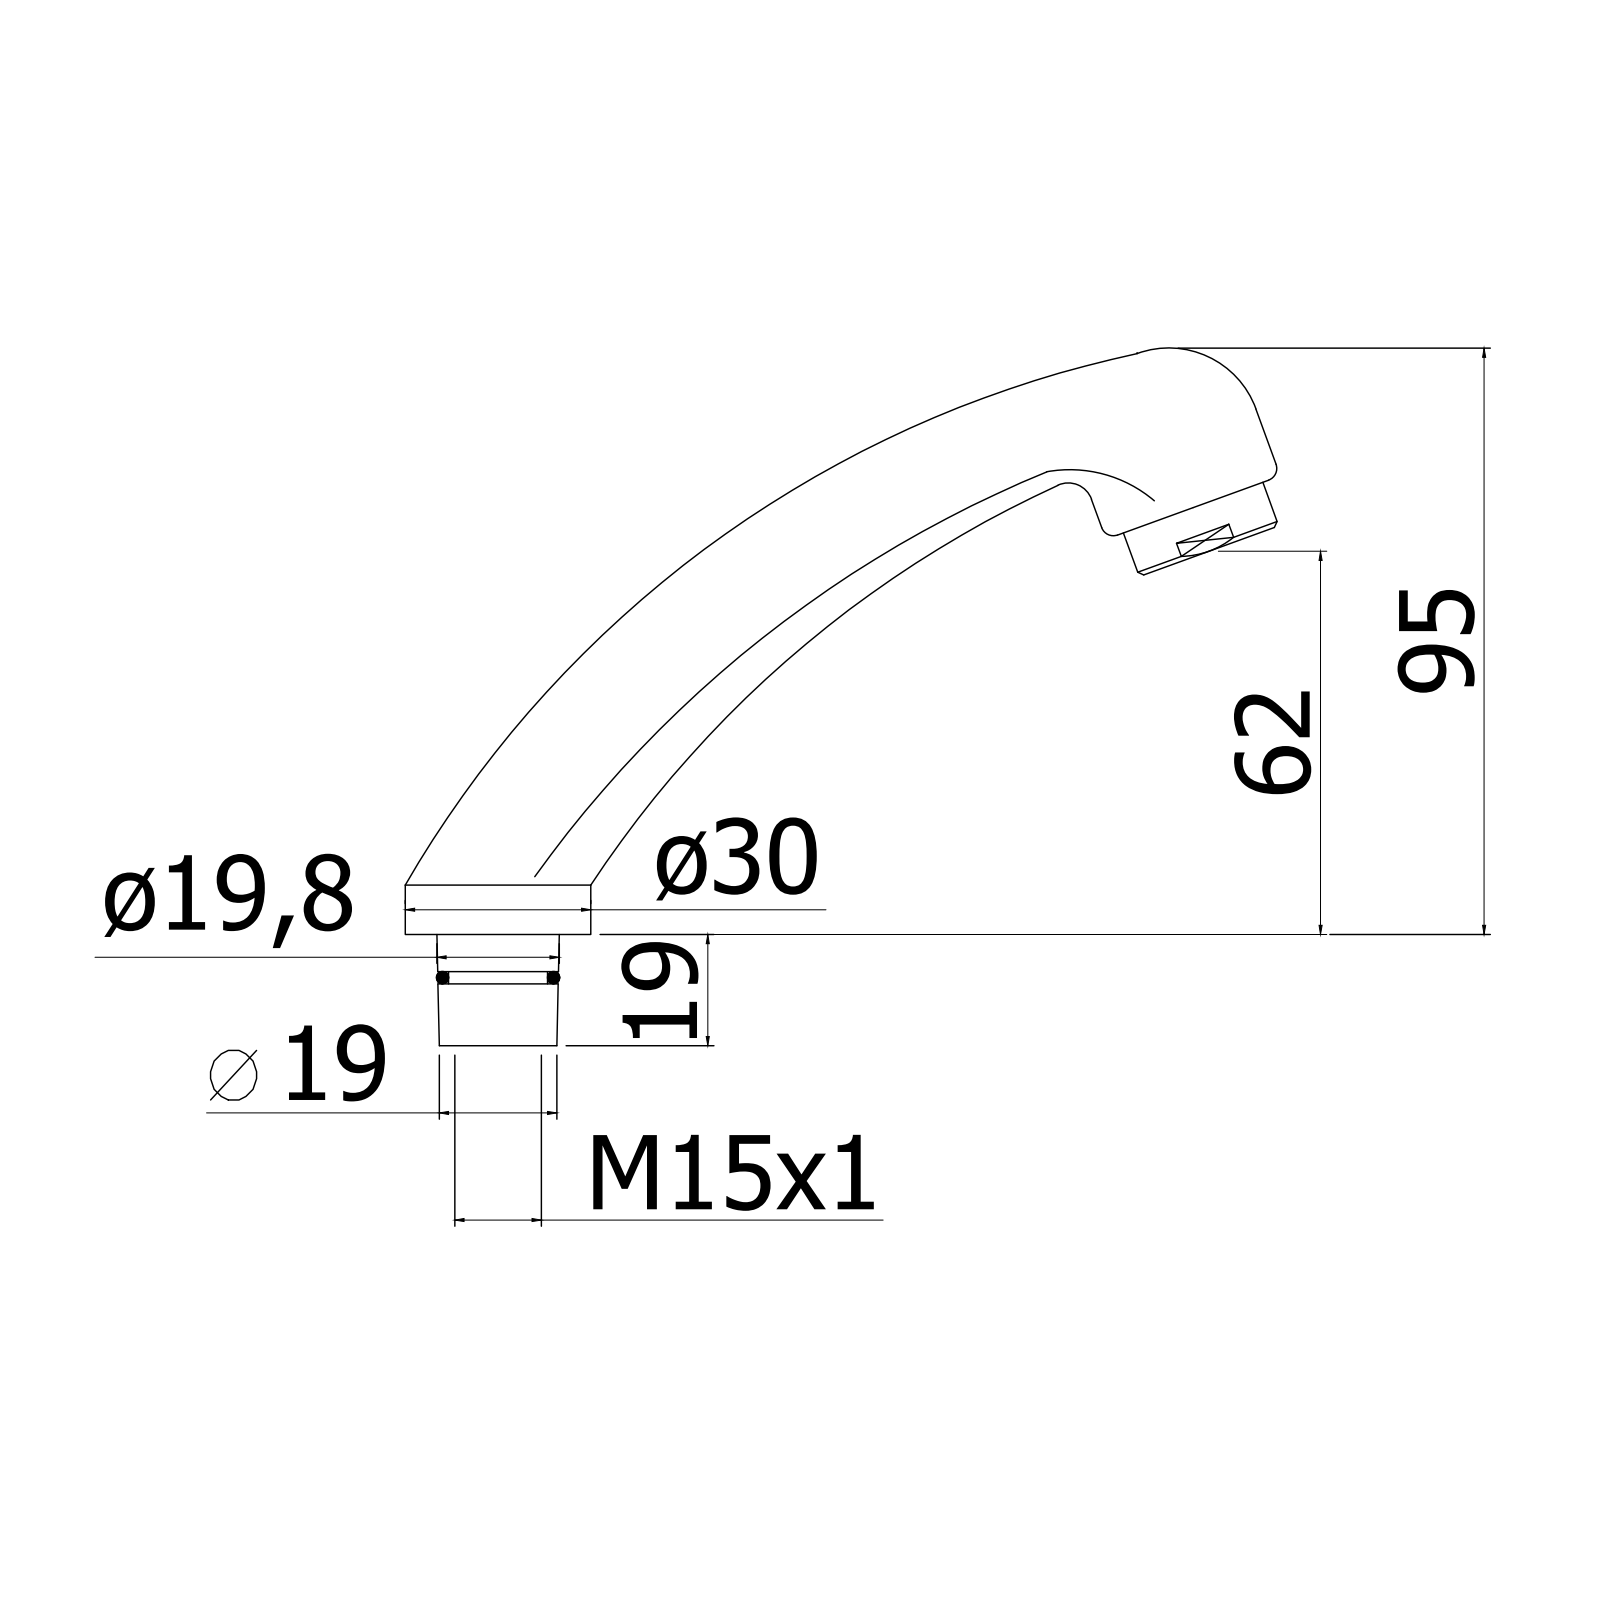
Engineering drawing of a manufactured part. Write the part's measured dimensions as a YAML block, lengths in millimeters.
part_name: "ZDOC014CR"
step_written_by: "CREO PARAMETRIC BY PTC INC, 2020044 (CONFIG_CONTROL_DESIGN)"
units: millimeters
bodies: {solids: 0, faces: 971, planar: 896, cylindrical: 29, other: 46}
overall_size: [155.84, 113.75, 32]
round_holes:
  - {diameter: 12, count: 1}
  - {diameter: 15, count: 1}
  - {diameter: 16, count: 1}
  - {diameter: 17, count: 1}
  - {diameter: 20, count: 1}
round_bosses_or_shafts:
  - {diameter: 31, count: 1}
  - {diameter: 24, count: 1}
  - {diameter: 19.5, count: 1}
  - {diameter: 18.8, count: 1}
  - {diameter: 16.8, count: 1}
partial_cylinders:
  - {radius: 4.75, count: 1}
face_to_face_distances: [2, 3, 9, 7.7, 1, 7, 10.7, 6, 0.5, 10]
